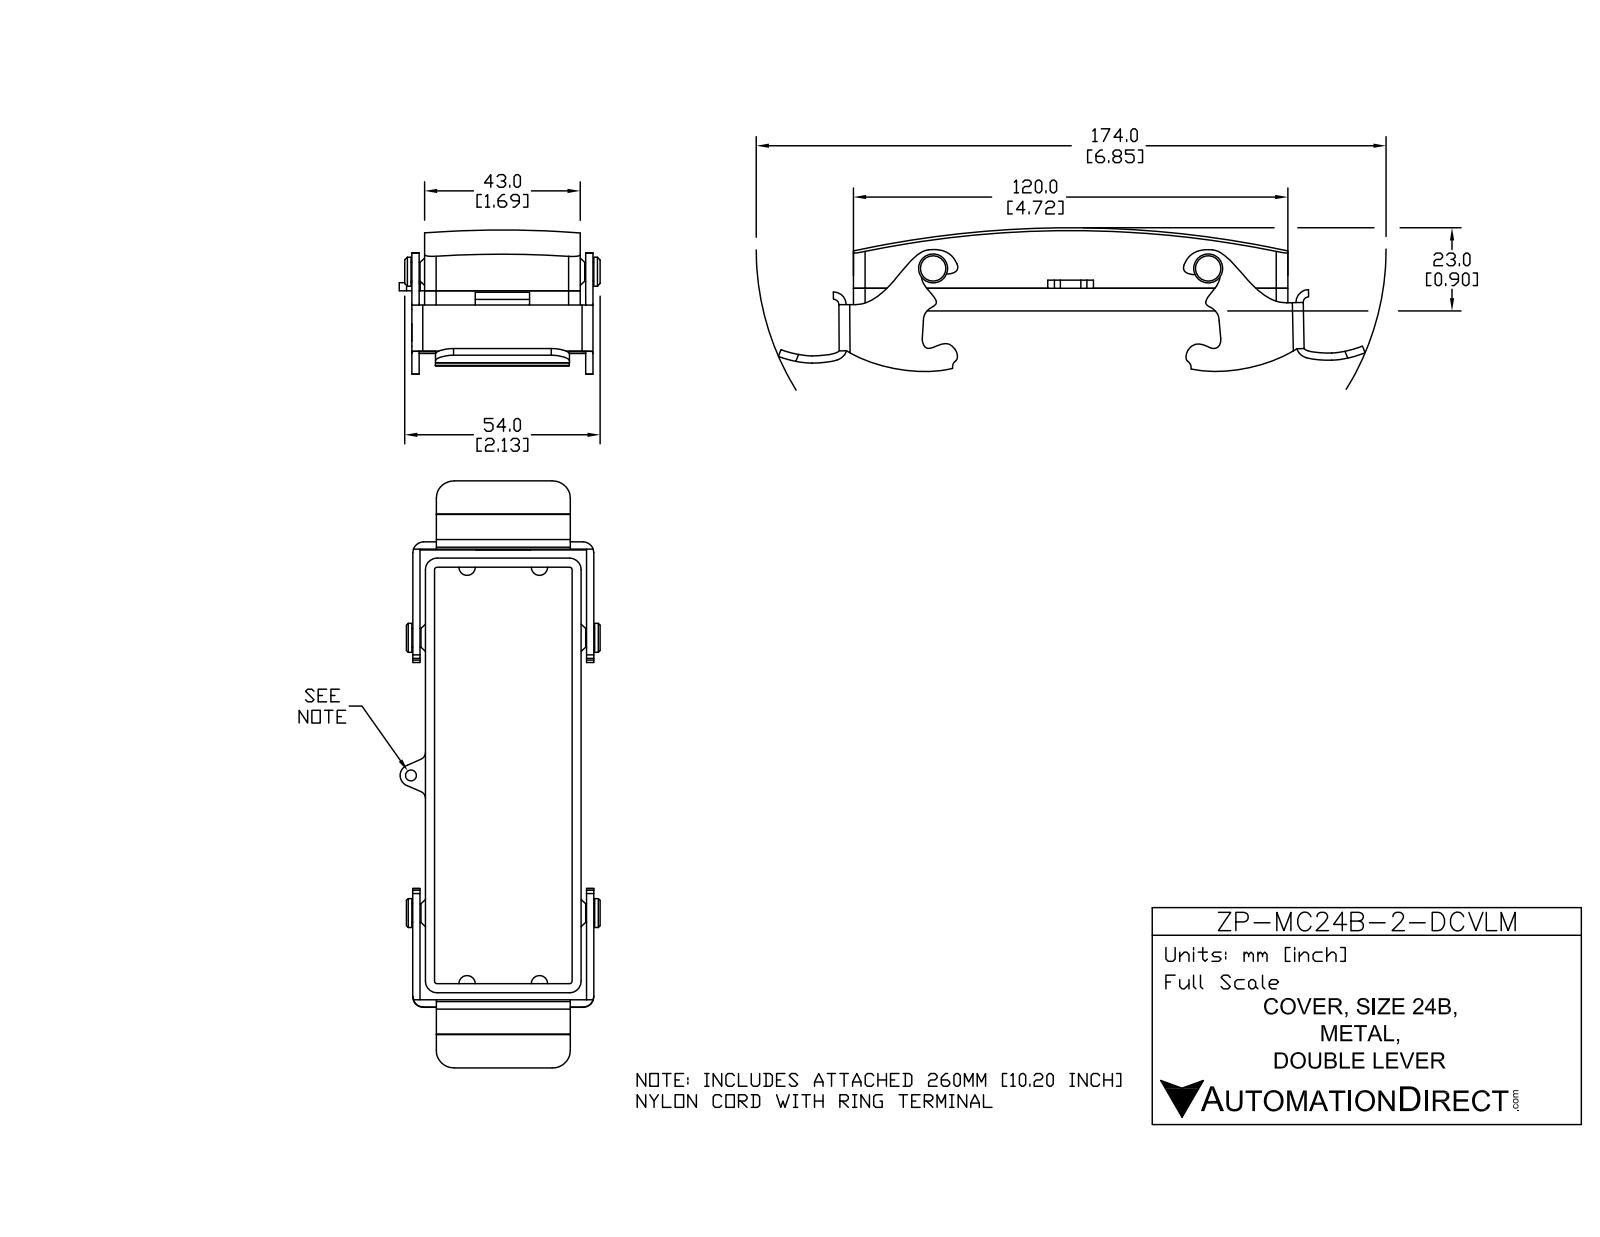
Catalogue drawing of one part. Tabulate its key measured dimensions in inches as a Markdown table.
| quantity | value |
| --- | --- |
| part name | ZP-MC24B-2-DCVLM |
| STEP written by | SolidWorks 2011 (AUTOMOTIVE_DESIGN) |
| units | inches |
| bodies | 6 solids, 256 faces (114 planar, 132 cylindrical, 10 other) |
| overall size | 6.003 × 2.175 × 1.776 |
| volume | 1.959 in³ |
| surface area | 54.33 in² |
| round holes (diameter × count) | 0.118 × 1 |
| round bosses / shafts (diameter × count) | 0.315 × 2, 0.204 × 2 |
| partial cylindrical surfaces (radius × count) | 0.039 × 12, 0.02 × 10, 0.079 × 8, 0.157 × 6, 0.028 × 4, 0.03 × 4, 0.089 × 4, 0.126 × 4 |
| main face-to-face distances | 0.098, 1.594, 0.039, 0.148, 1.742, 1.644, 0.187, 0.089, 0.049, 1.683 |
